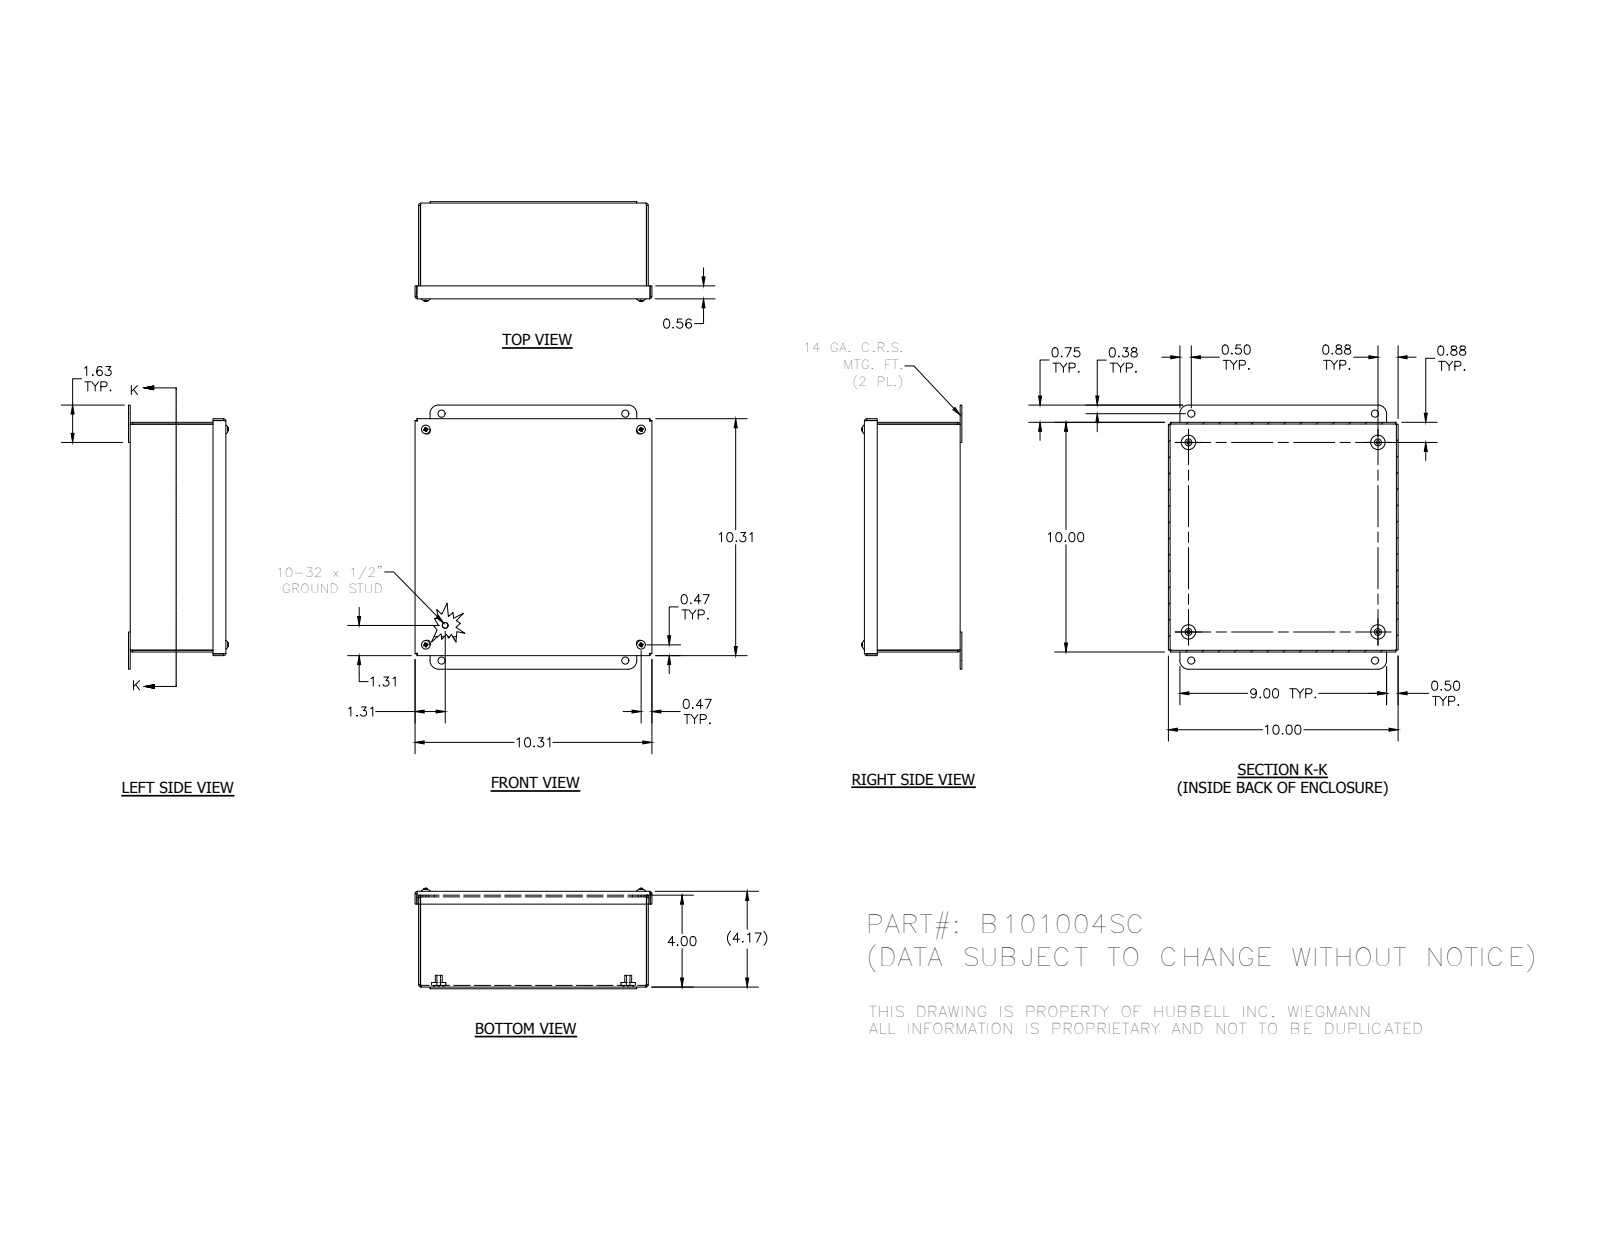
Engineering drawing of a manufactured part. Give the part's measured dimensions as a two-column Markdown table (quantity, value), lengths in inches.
| quantity | value |
| --- | --- |
| part name | B101004SC; 3484; 34984; B101004SCBKP (+6 more) |
| STEP written by | Autodesk Inventor 2012 (AUTOMOTIVE_DESIGN) |
| units | inches |
| bodies | 23 solids, 532 faces (311 planar, 102 cylindrical, 119 other) |
| overall size | 11.5 × 10.313 × 4.346 |
| volume | 36.44 in³ |
| surface area | 928.9 in² |
| round holes (diameter × count) | 0.145 × 4, 0.156 × 4, 0.196 × 4, 0.278 × 4, 0.281 × 4, 0.31 × 4, 0.313 × 4 |
| round bosses / shafts (diameter × count) | 0.19 × 5, 0.625 × 4, 0.453 × 4, 0.406 × 4, 0.373 × 4, 0.3 × 4, 0.248 × 4, 0.25 × 1 |
| partial cylindrical surfaces (radius × count) | 0.031 × 12, 0.105 × 12, 0.089 × 4, 0.375 × 4 |
| main face-to-face distances | 0.074, 4.094, 9.926, 4.168, 4.02, 9.852, 10, 0.075, 0.149, 4.169 |
| hole center spacings | 9.314, 8.83, 9.374, 9.375, 8.714, 9.395, 13.172, 0.087 |
